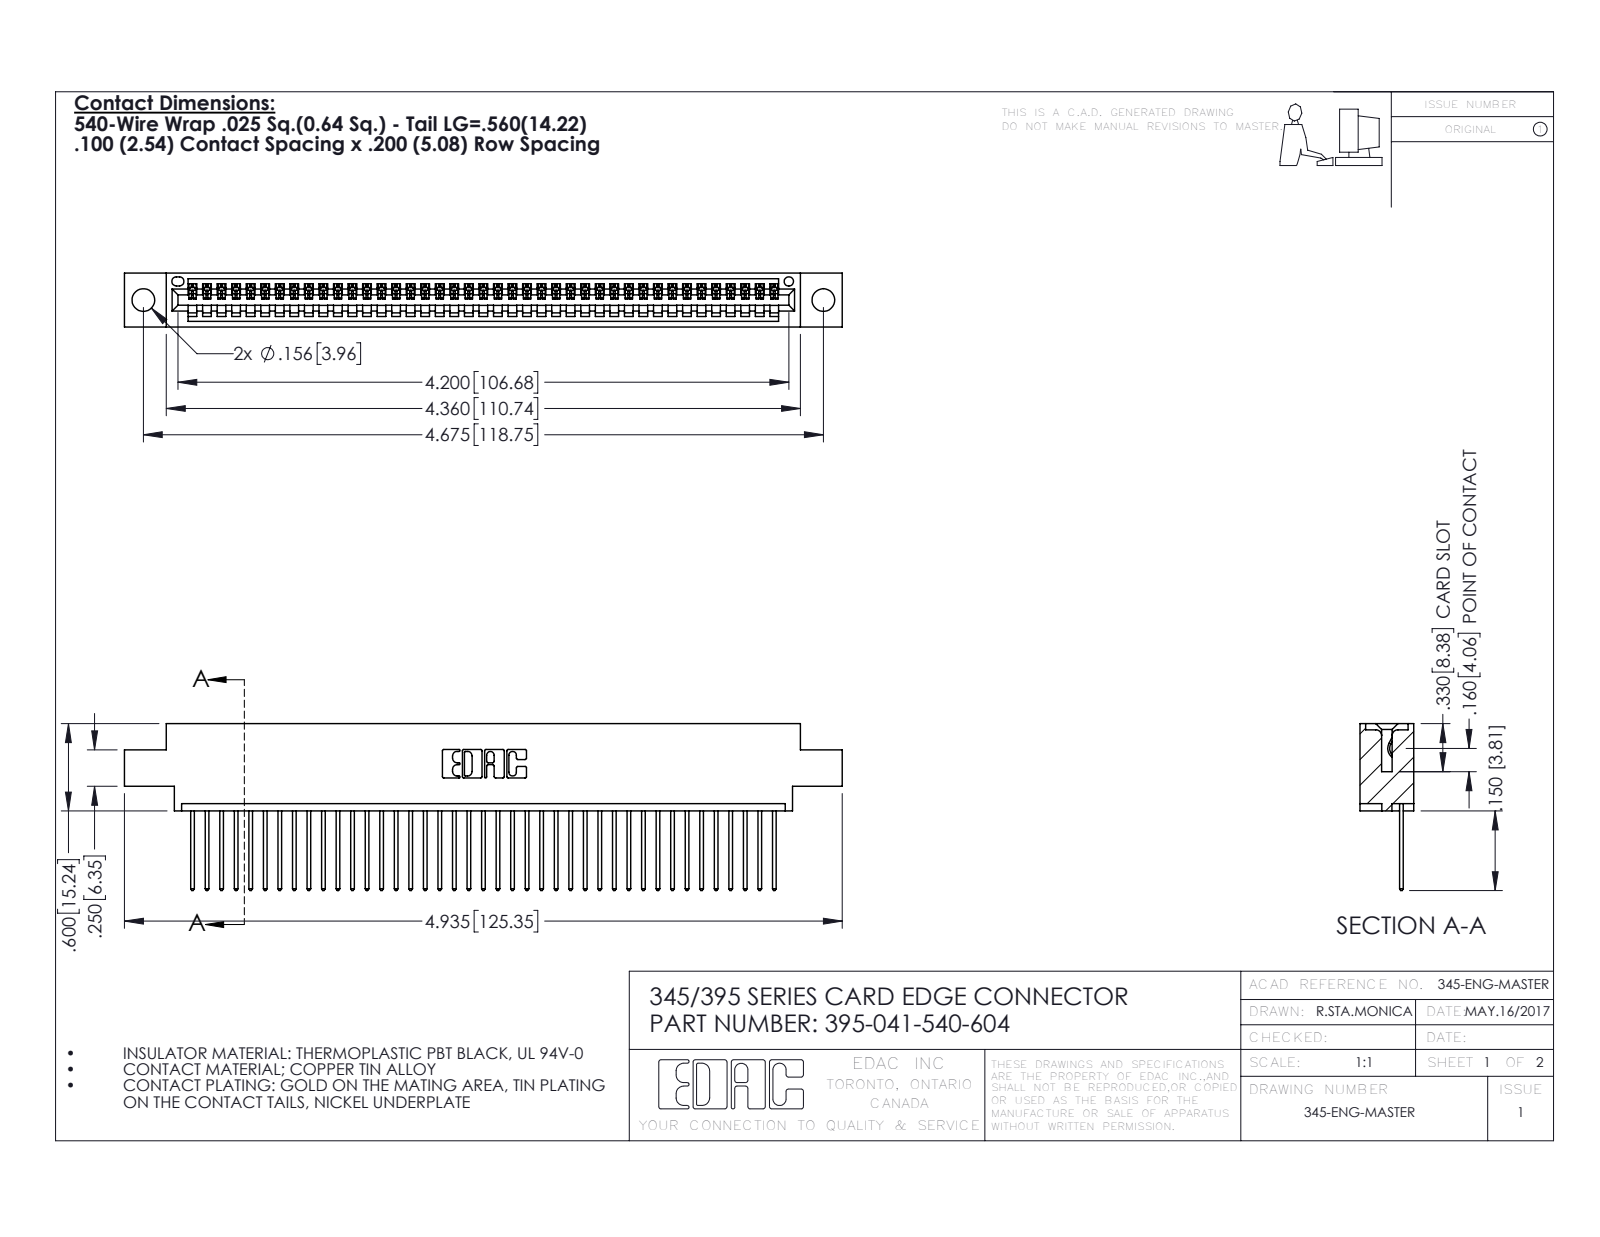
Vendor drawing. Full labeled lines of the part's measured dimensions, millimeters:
Part name (STEP PRODUCT): 345 Part_0.170 Offset - 0.156 Dia-TH; 345-292-001_345-293-140; 395-041-540-604
STEP written by: SolidWorks 2016 (CONFIG_CONTROL_DESIGN)
Units: millimetres
Bodies: 42 solids, 2508 faces (1724 planar, 784 cylindrical, 0 other)
Overall size (bounding box): 125.3 × 29.1 × 9.4
Volume: 11 700 mm³ · Surface area: 15 940 mm²
Round holes (diameter × count): ⌀4 ×2, ⌀1.6 ×1
Partial cylindrical surfaces — rounded edges, fillets, slot ends (radius × count): R0.2 ×82, R0.3 ×82, R0.3 ×22, R0.2 ×6, R0.8 ×6, R0.7 ×3, R0.8 ×2, R1 ×2
Main face-to-face distances: 7.6, 1.8, 9.4, 2.5, 6.9, 0.6, 5.1, 5.7, 4.4, 3.8
Hole centre spacings: 6.9, 112.8, 118.7
